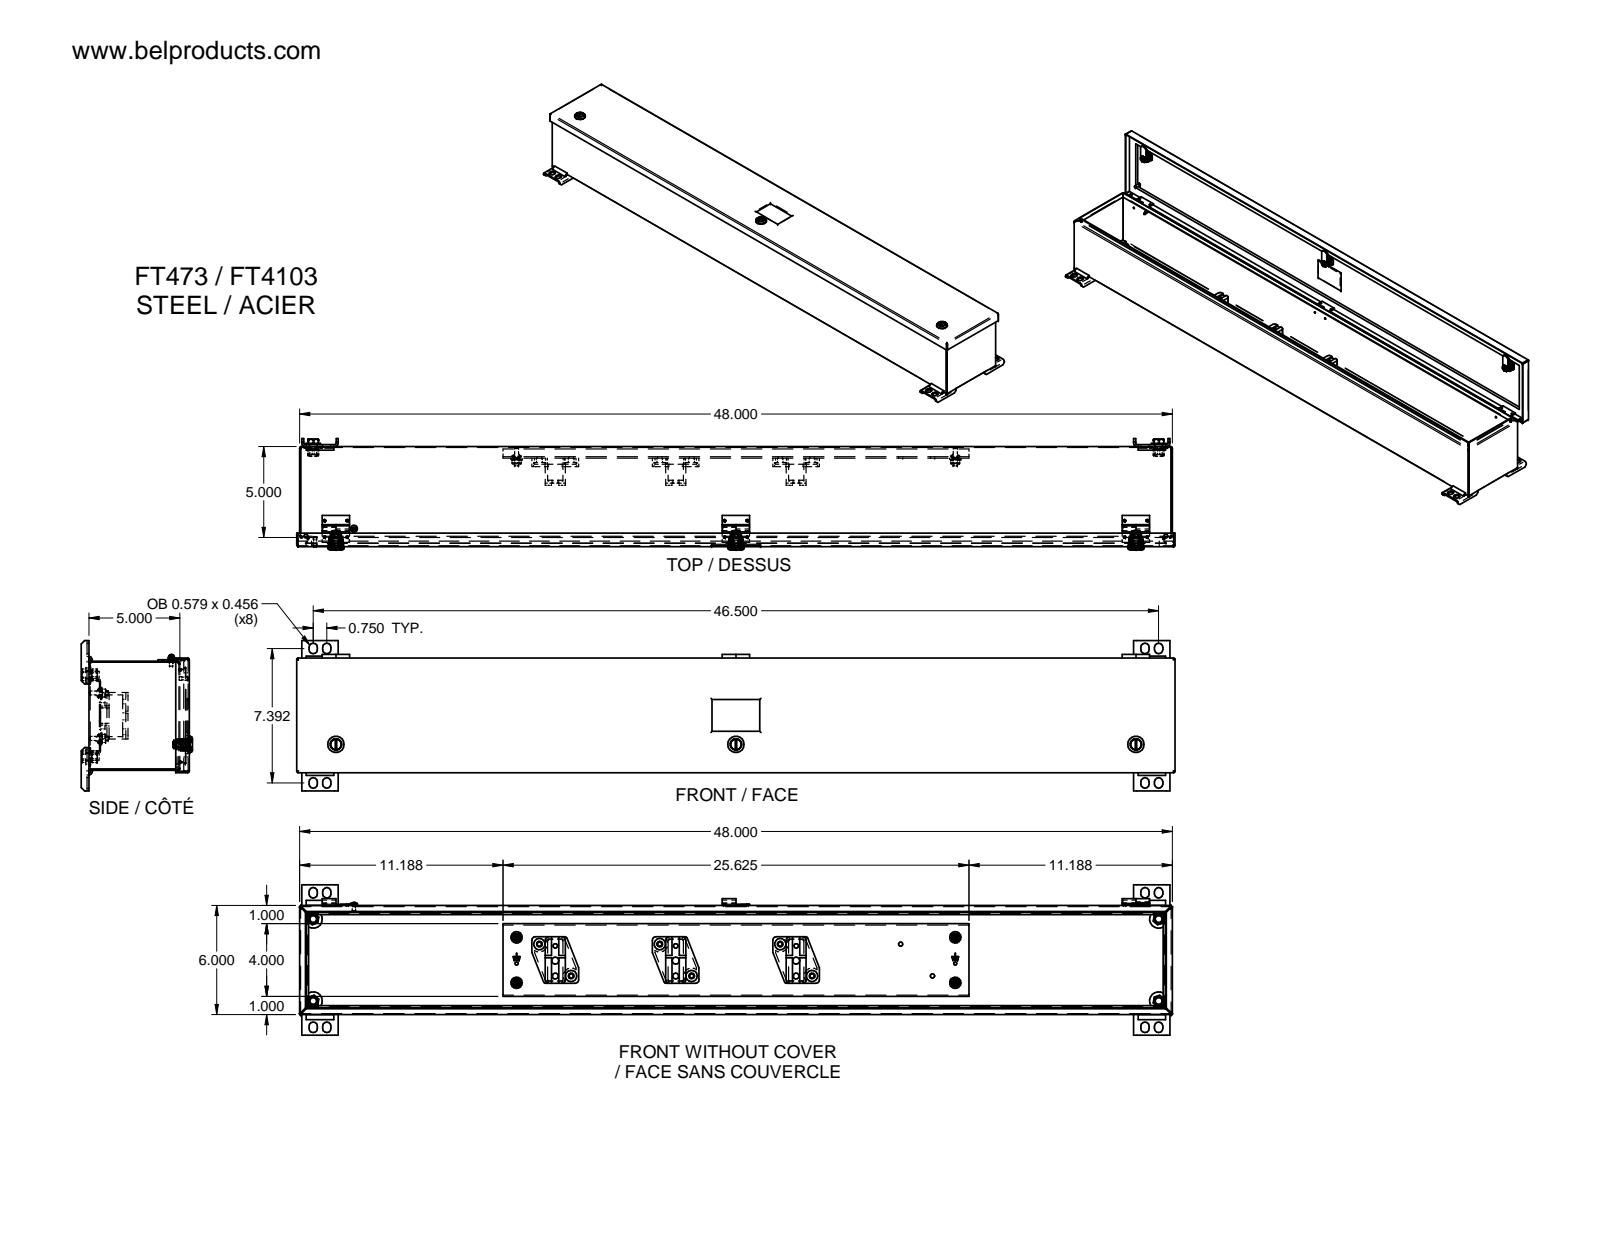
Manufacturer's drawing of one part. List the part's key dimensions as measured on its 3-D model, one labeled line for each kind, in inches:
Part name (STEP PRODUCT): LOCK AVEC TOURNEVIS TYPE 4-12 SANS CAME-oa8; HOSING-oa0; INSERT POUR TOURNEVIS-oa1; NOIX DE FIXATION-oa2 (+8 more)
STEP written by: Unknown (AUTOMOTIVE_DESIGN)
Units: inches
Bodies: 79 solids, 2953 faces (1705 planar, 587 cylindrical, 661 other)
Overall size (bounding box): 48.3 × 8.266 × 6.125
Volume: 117.6 in³ · Surface area: 3 260 in²
Round holes (diameter × count): ⌀0.124 ×12, ⌀0.13 ×12, ⌀0.236 ×8, ⌀0.375 ×8, ⌀0.456 ×8, ⌀0.25 ×7, ⌀0.312 ×6, ⌀0.625 ×6, ⌀0.125 ×5, ⌀0.281 ×4, ⌀0.355 ×4, ⌀0.406 ×4
Round bosses / shafts (diameter × count): ⌀0.125 ×12, ⌀0.119 ×5, ⌀0.812 ×4, ⌀0.625 ×4, ⌀0.219 ×4, ⌀0.031 ×4, ⌀0.9 ×3, ⌀0.89 ×3
Partial cylindrical surfaces — rounded edges, fillets, slot ends (radius × count): R0.375 ×32, R0.01 ×24, R0.187 ×22, R0.032 ×18, R0.092 ×16, R0.228 ×16, R0.057 ×12, R0.06 ×8
Main face-to-face distances: 0.06, 5.94, 0.06, 5.454, 5.514, 5.394, 5.454, 6, 5.88, 0.075
Hole centre spacings: 0.907, 22, 6.625, 6.625, 13.25, 22.019, 1.25, 1.544
